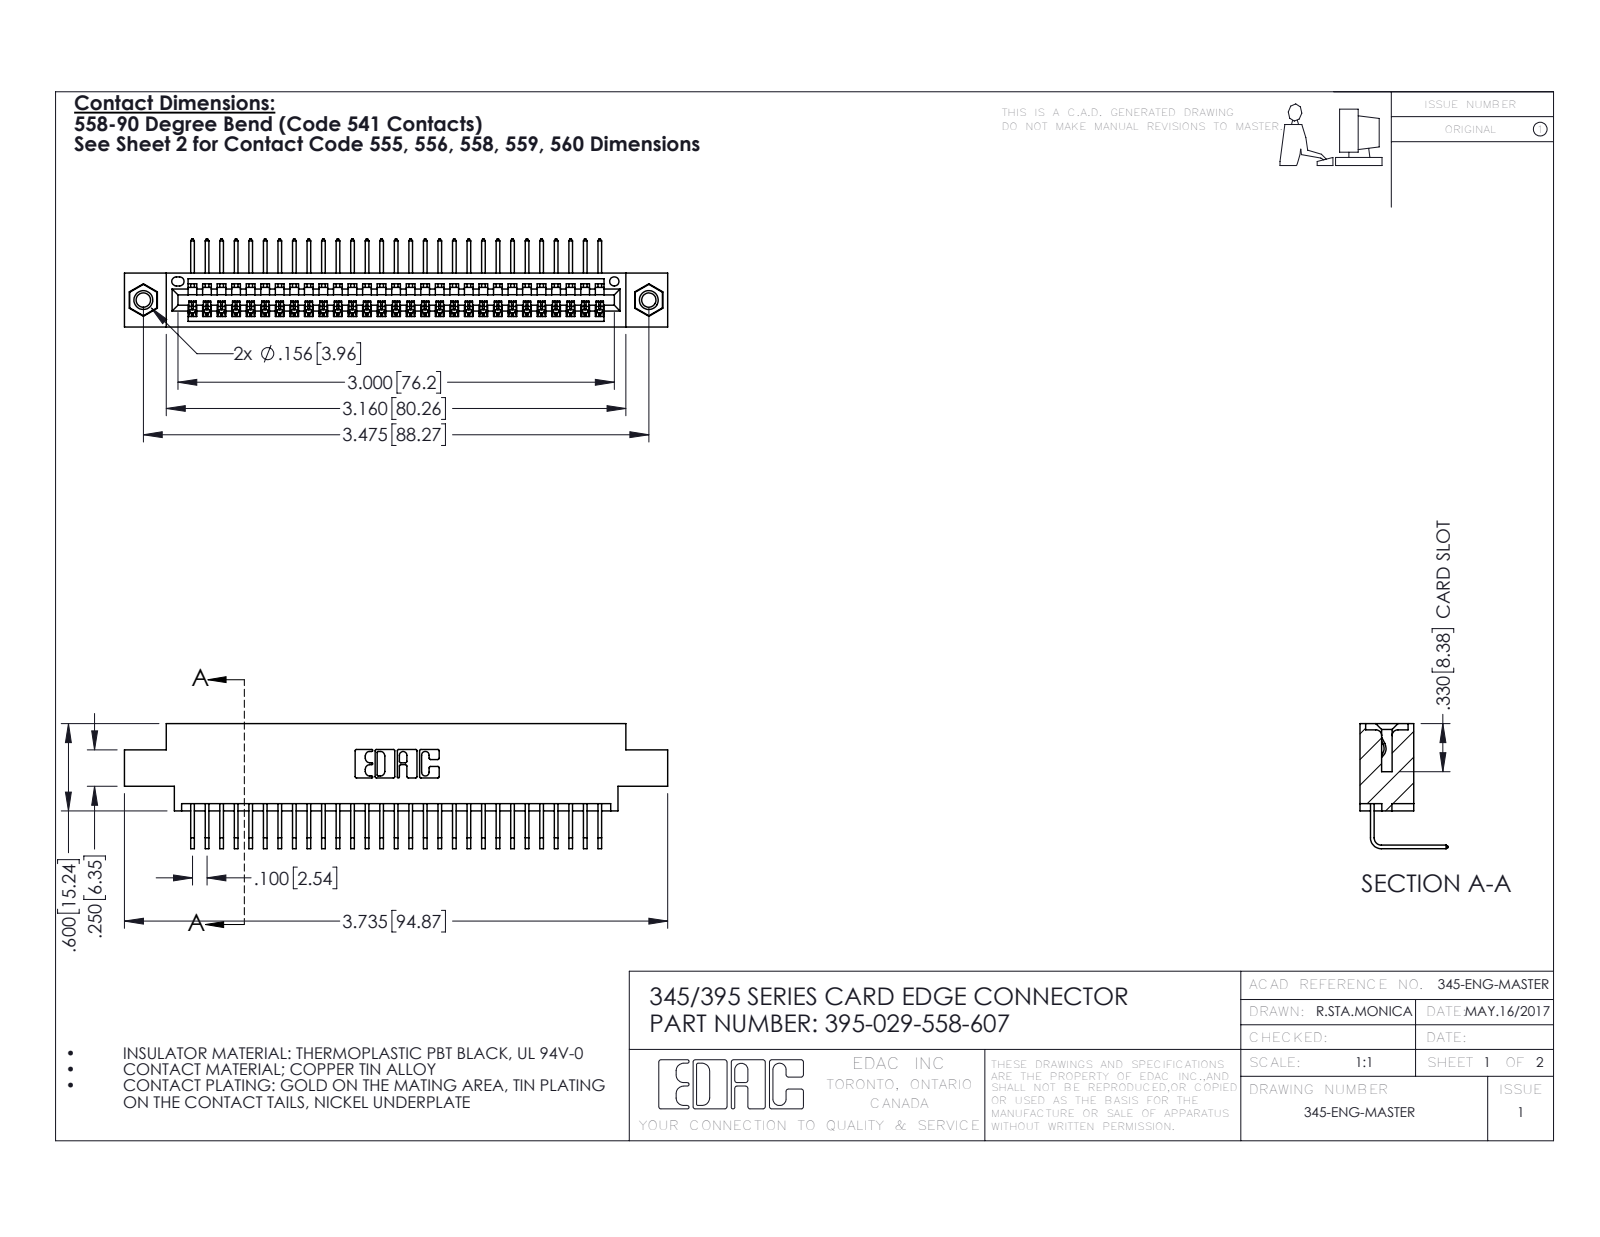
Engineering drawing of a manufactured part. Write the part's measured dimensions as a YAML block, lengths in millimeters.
part_name: "395-029-558-607; 345-250-001_345-250-005-103; 345 Part_0.170 Offset - 0.156 Dia-TI; 345-292-001_558 Tail - 2"
step_written_by: "SolidWorks 2016 (CONFIG_CONTROL_DESIGN)"
units: millimeters
bodies: {solids: 32, faces: 1930, planar: 1334, cylindrical: 580, other: 16}
overall_size: [94.9, 21.8, 15.4]
volume: 8880
surface_area: 12340
round_holes:
  - {diameter: 2.5, count: 2}
  - {diameter: 3.2, count: 2}
  - {diameter: 4, count: 2}
  - {diameter: 1.6, count: 1}
round_bosses_or_shafts:
  - {diameter: 3.9, count: 2}
partial_cylinders:
  - {radius: 0.2, count: 58}
  - {radius: 0.3, count: 22}
  - {radius: 0.2, count: 6}
  - {radius: 0.8, count: 6}
  - {radius: 0.7, count: 3}
  - {radius: 0.8, count: 2}
  - {radius: 1, count: 2}
  - {radius: 0.4, count: 1}
face_to_face_distances: [1.8, 7.6, 9.4, 5.1, 2.5, 6.9, 0.6, 5.7, 4.4, 3.8]
hole_center_spacings: [6.9, 82.3, 88.3]
